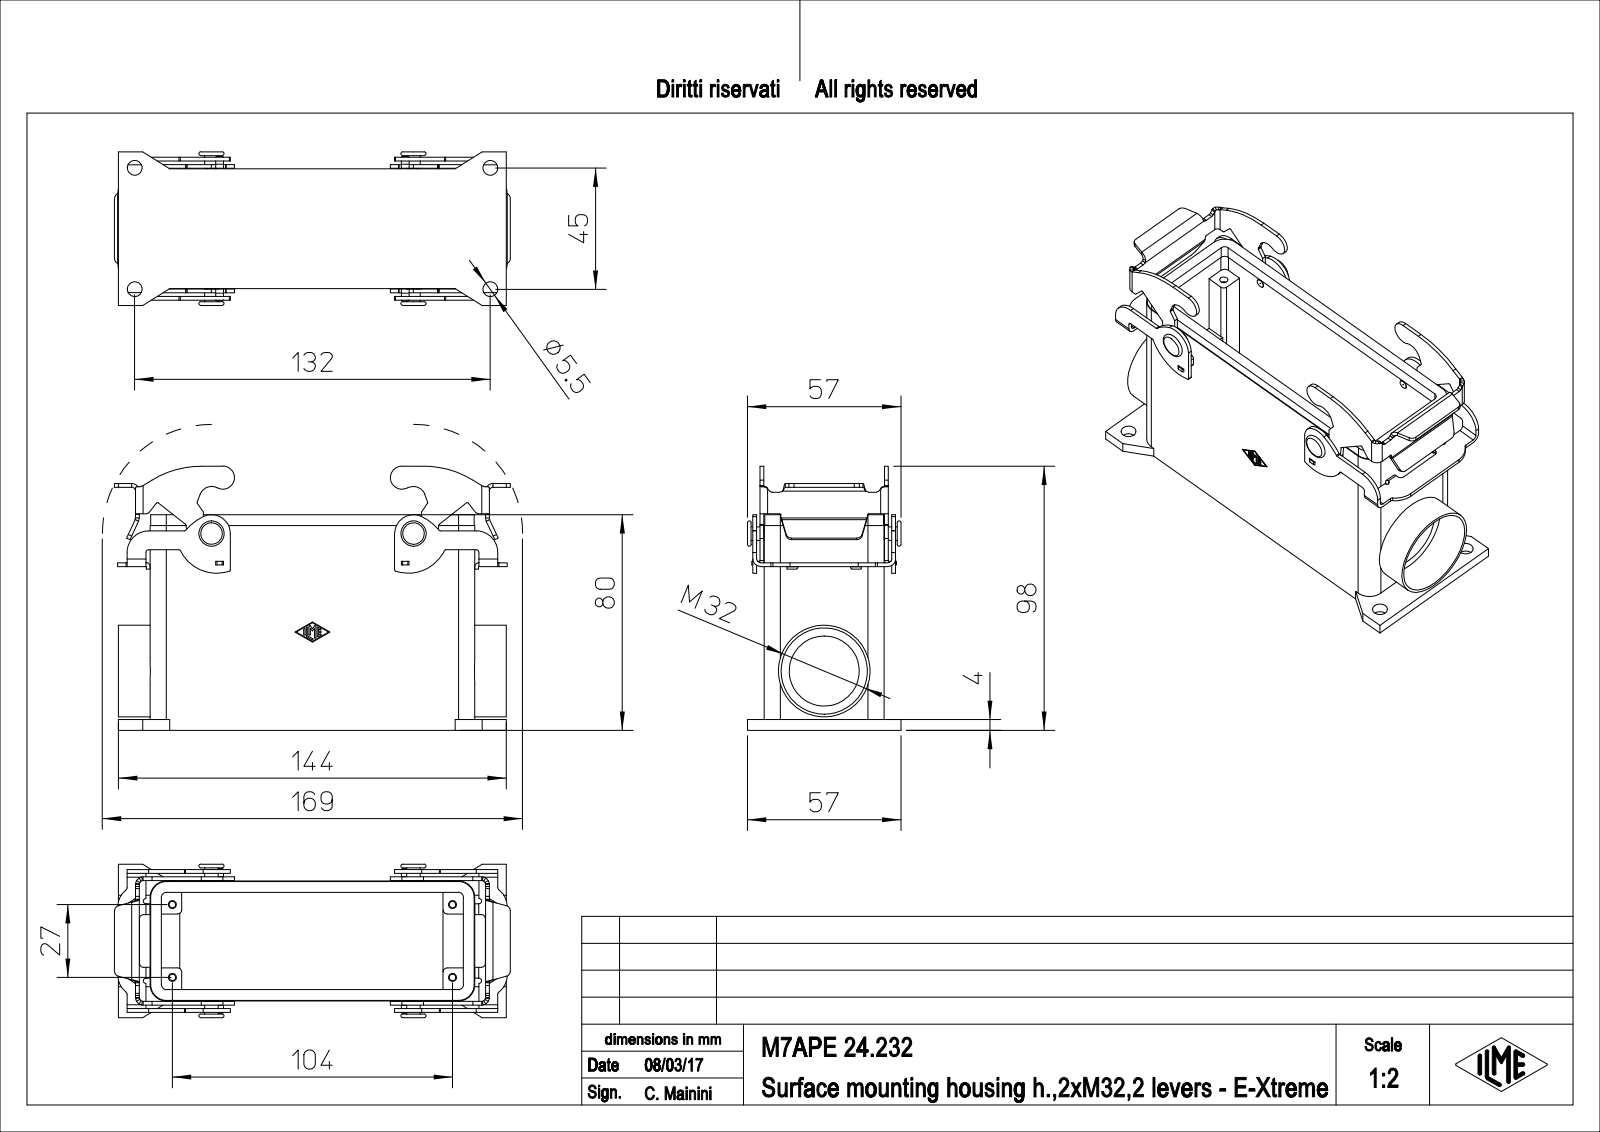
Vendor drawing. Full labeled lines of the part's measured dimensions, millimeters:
Part name (STEP PRODUCT): M7APE_24.232
STEP written by: PTC Creo Elements/Direct Modeling 19.0E 27-Jun-2016 (C) Parametric Technology GmbH (AUTOMOTIVE_DESIGN)
Units: millimetres
Bodies: 1 solid, 601 faces (291 planar, 270 cylindrical, 40 other)
Overall size (bounding box): 146.97 × 98 × 57
Volume: 158 851 mm³ · Surface area: 84 127 mm²
Round holes (diameter × count): ⌀2.46 ×4, ⌀3 ×4, ⌀5.5 ×4, ⌀26 ×1, ⌀32 ×1
Round bosses / shafts (diameter × count): ⌀5 ×2, ⌀3 ×2, ⌀43 ×1
Partial cylindrical surfaces — rounded edges, fillets, slot ends (radius × count): R0.5 ×22, R1 ×20, R0.25 ×16, R1.5 ×14, R2 ×12, R1.4 ×10, R2.8 ×10, R8 ×6
Main face-to-face distances: 4, 40.5, 44.5, 36.5, 1.4, 11.75, 2.7, 48.9, 120.5, 8.25
Hole centre spacings: 16.64, 38.63, 118.34, 123.37, 27, 45, 104, 107.45
